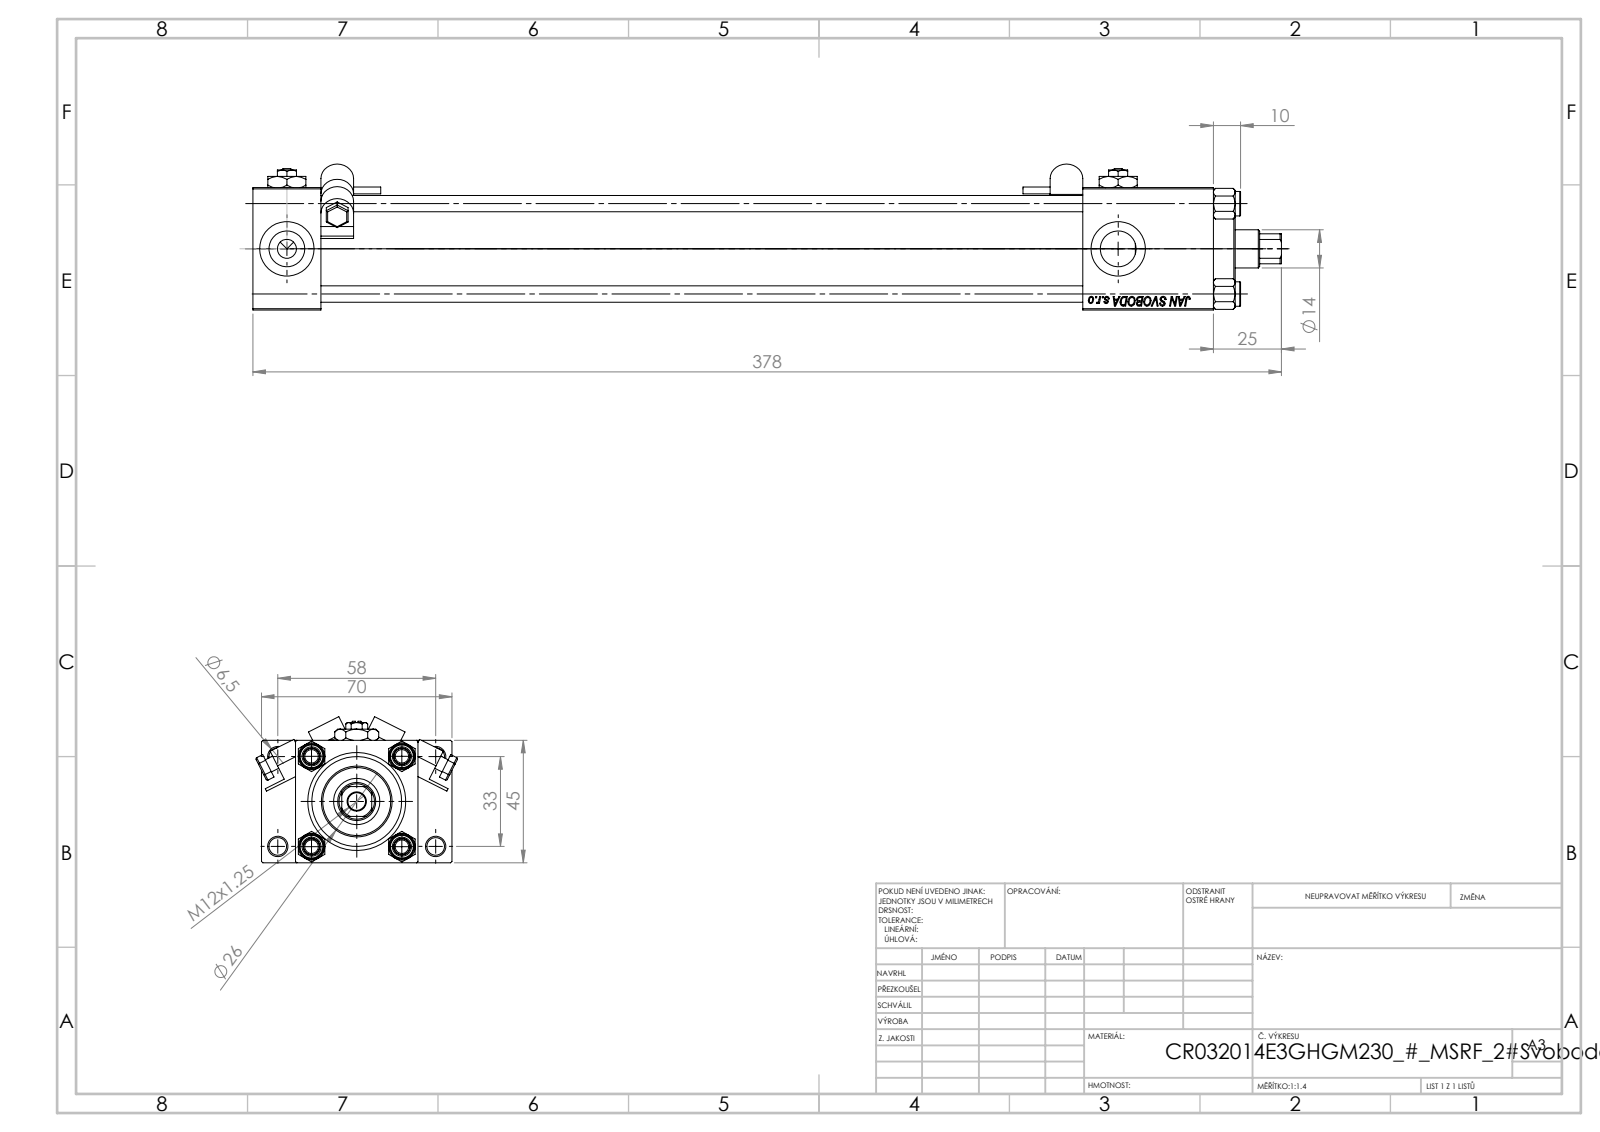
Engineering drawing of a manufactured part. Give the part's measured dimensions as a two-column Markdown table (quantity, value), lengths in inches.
| quantity | value |
| --- | --- |
| part name | MSRF_MSRG1; NUT_M5_E; V215_VC_A; V215CR_VCP_E (+3 more) |
| STEP written by | SolidWorks 2019 (CONFIG_CONTROL_DESIGN) |
| units | inches |
| bodies | 15 solids, 1299 faces (580 planar, 125 cylindrical, 594 other) |
| overall size | 14.882 × 2.915 × 2.113 |
| volume | 22.09 in³ |
| surface area | 248.7 in² |
| round holes (diameter × count) | 0.256 × 5, 0.236 × 4, 0.518 × 4, 0.787 × 4, 0.276 × 3, 0.551 × 1, 0.669 × 1, 0.945 × 1, 1.26 × 1, 1.299 × 1 |
| round bosses / shafts (diameter × count) | 0.354 × 4, 0.197 × 2, 0.098 × 2, 1.496 × 1, 1.024 × 1 |
| partial cylindrical surfaces (radius × count) | 0.02 × 12, 0.236 × 4, 0.256 × 1 |
| main face-to-face distances | 1.772, 0.984, 0.492, 2.264, 13.898, 12.913, 12.008, 11.024, 1.89, 12.768 |
| hole center spacings | 0.488, 0.924, 1.307, 1.314, 1.392, 1.795, 2.219, 1.299 |
